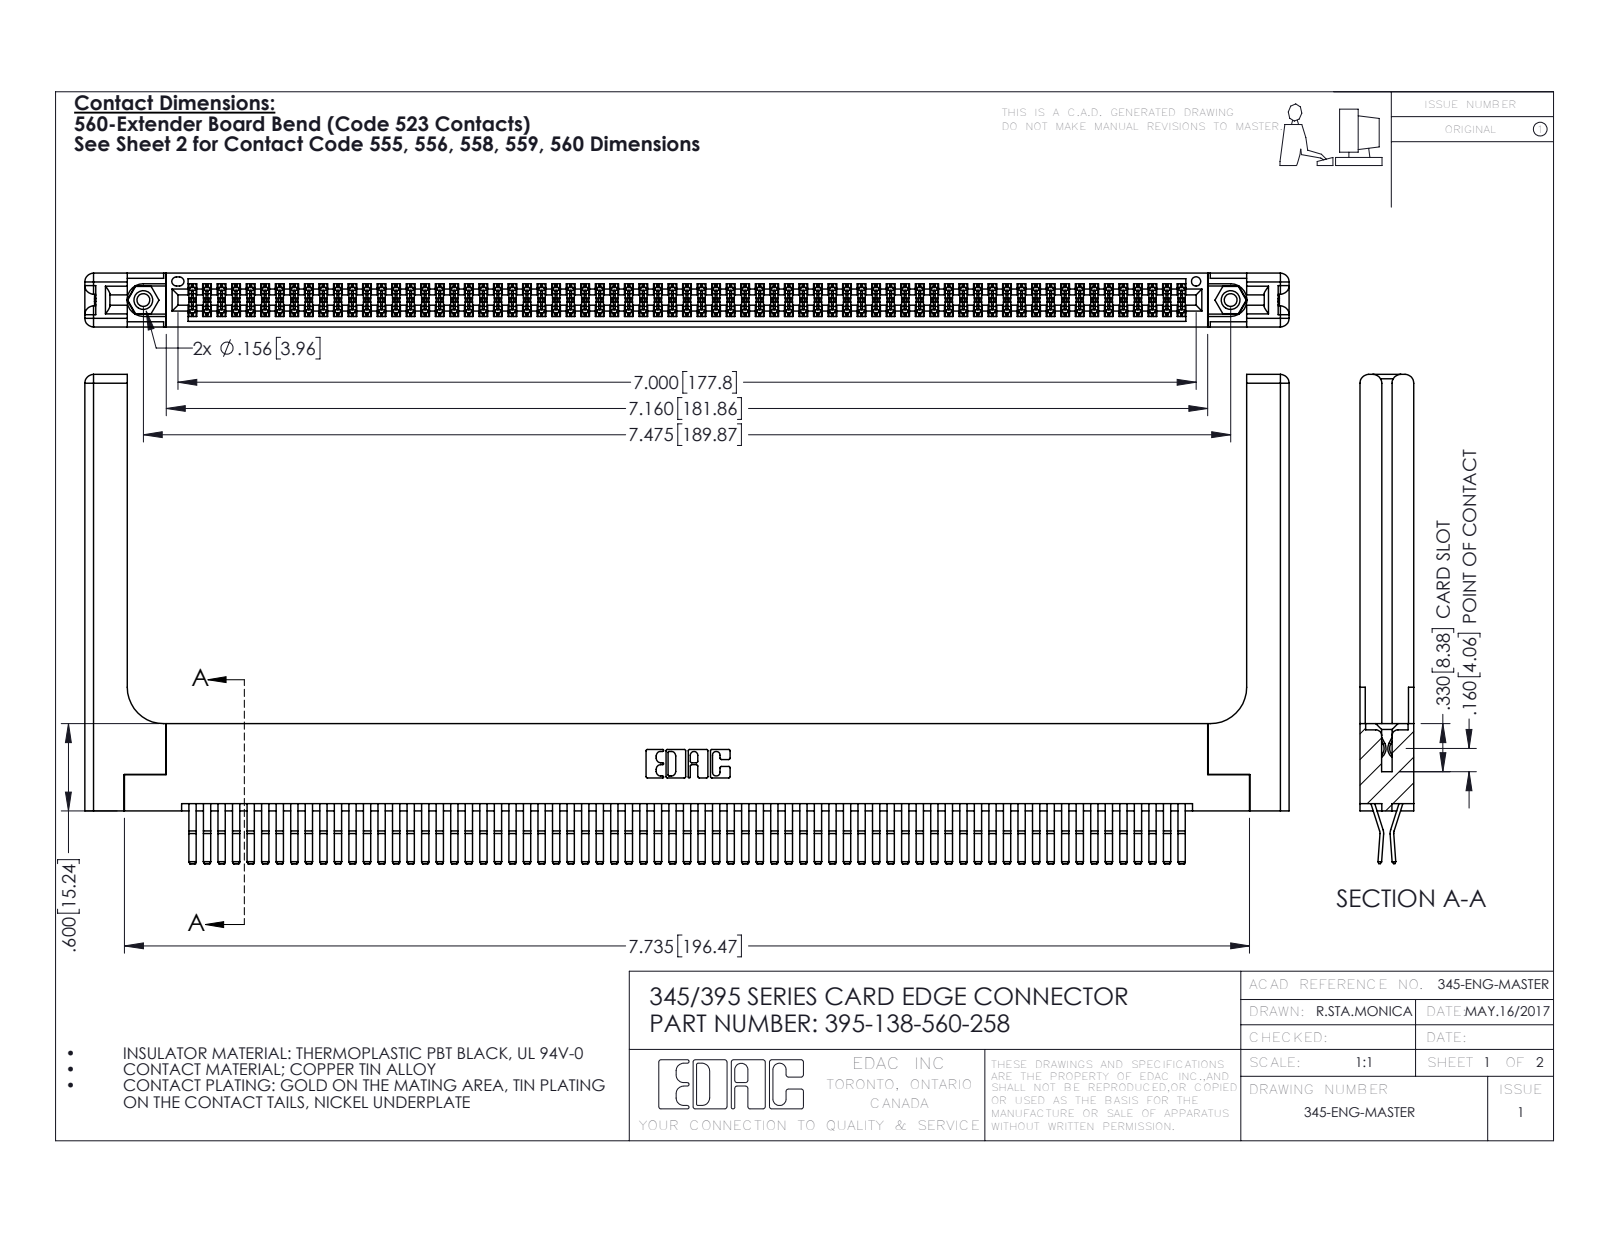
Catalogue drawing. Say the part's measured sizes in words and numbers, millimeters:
The part is named "345-292-001_560 Tail; 345 Part_Flush Mounting Lugs - 0.156 Dia-TH; 345-220-058_345-220-058; 345-250-001_345-250-001-102 (+1 more)". Its 3-D file was written by "SolidWorks 2016 (CONFIG_CONTROL_DESIGN)". It is 143 solids with 7558 faces: 4782 planar, 2716 cylindrical and 60 other. Overall it measures 210.3 by 85.4 by 9.4 millimeters. Its volume is 30 050 cubic millimeters and its surface area 39 810 square millimeters. Round holes: 2 of diameter 2.3, 2 of diameter 3.2, 2 of diameter 4, 1 of diameter 1.6. Round bosses or shafts: 2 of diameter 3.9. Partial cylindrical surfaces (rounded edges, fillets, slot ends): 207 of radius 0.2, 22 of radius 0.3, 16 of radius 1.5, 6 of radius 0.2, 6 of radius 0.8, 3 of radius 0.7, 2 of radius 0.3, 2 of radius 0.4. The main face-to-face distances are 1.8, 7.6, 0.6, 9.4, 5.1, 2.5, 6.9, 5.7, 3.8, 3.8. The hole center spacings are 6.9, 183.9, 189.9.
